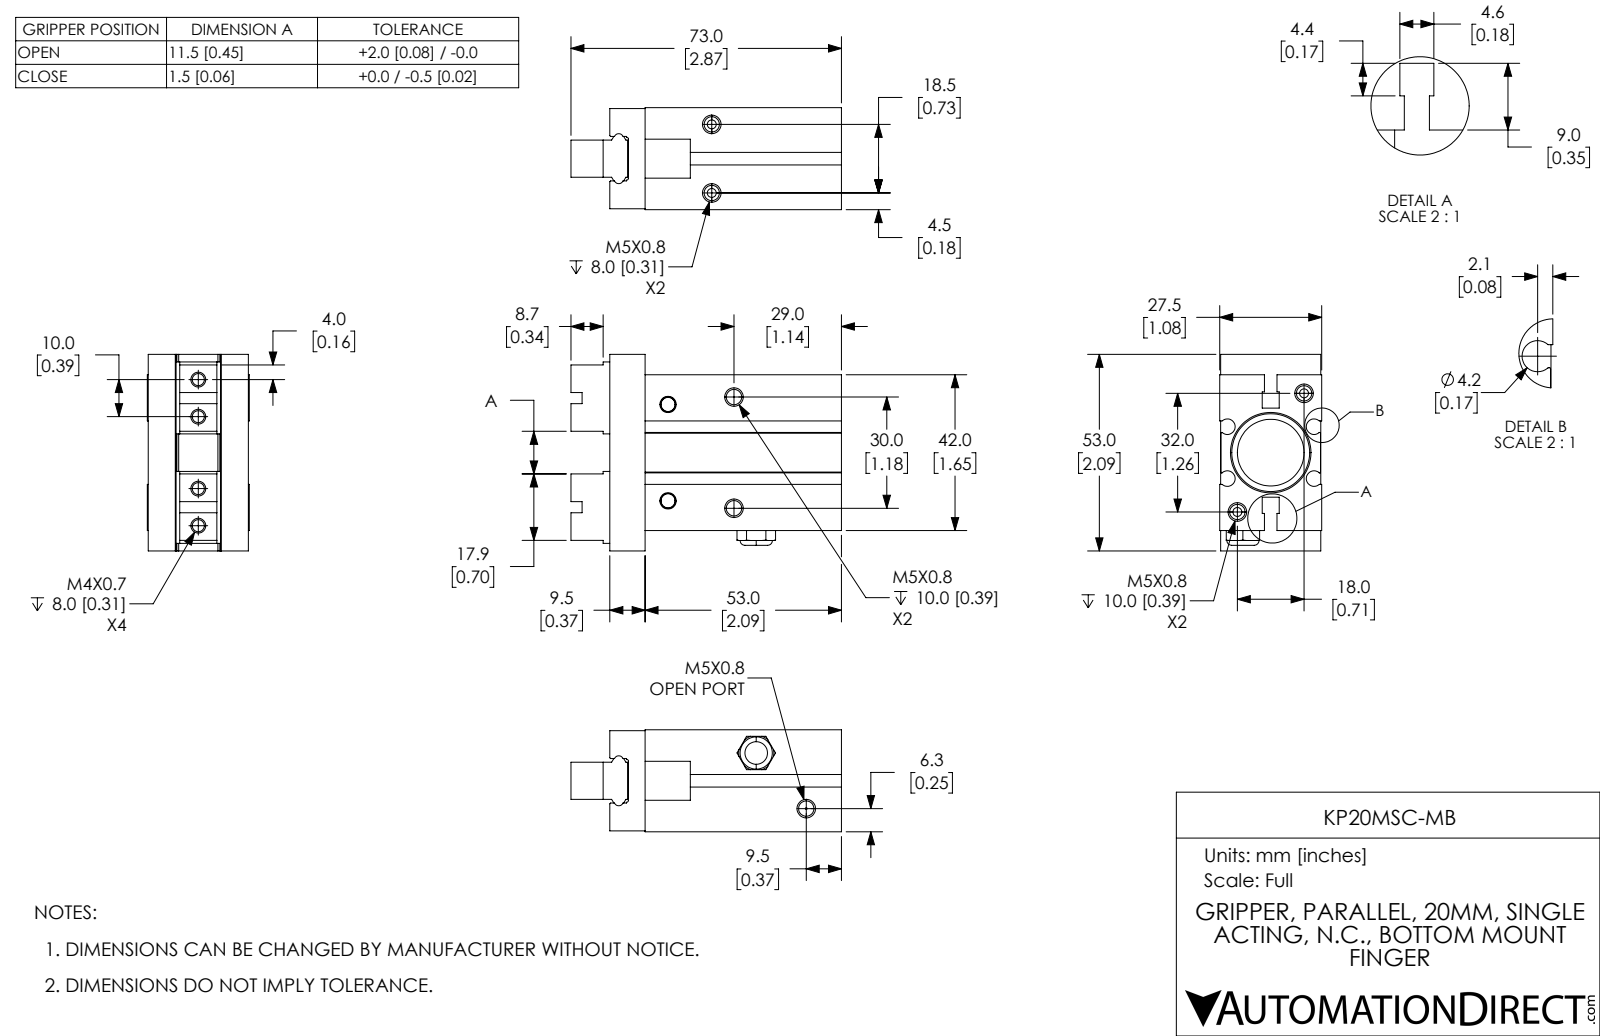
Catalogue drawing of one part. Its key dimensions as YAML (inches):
part_name: "KP20MSC-MB; KP20MSC-MB-1; KP20MSC-MB-2; KP20MSC-MB-3"
step_written_by: "SolidWorks 2017 (CONFIG_CONTROL_DESIGN)"
units: inches
bodies: {solids: 3, faces: 265, planar: 137, cylindrical: 66, other: 62}
overall_size: [2.874, 2.087, 1.083]
volume: 3.867
surface_area: 33.69
round_holes:
  - {diameter: 0.163, count: 8}
  - {diameter: 0.128, count: 4}
  - {diameter: 0.02, count: 2}
  - {diameter: 0.198, count: 2}
  - {diameter: 0.24, count: 1}
  - {diameter: 0.709, count: 1}
  - {diameter: 0.827, count: 1}
partial_cylinders:
  - {radius: 0.008, count: 8}
  - {radius: 0.049, count: 4}
  - {radius: 0.083, count: 4}
  - {radius: 0.02, count: 2}
face_to_face_distances: [0.335, 0.738, 1.083, 1.654, 1.071, 0.748, 0.323, 0.736, 0.325, 1.073]
hole_center_spacings: [0.382, 0.383, 0.394, 0.433, 0.723, 0.776, 1.072, 1.157]
